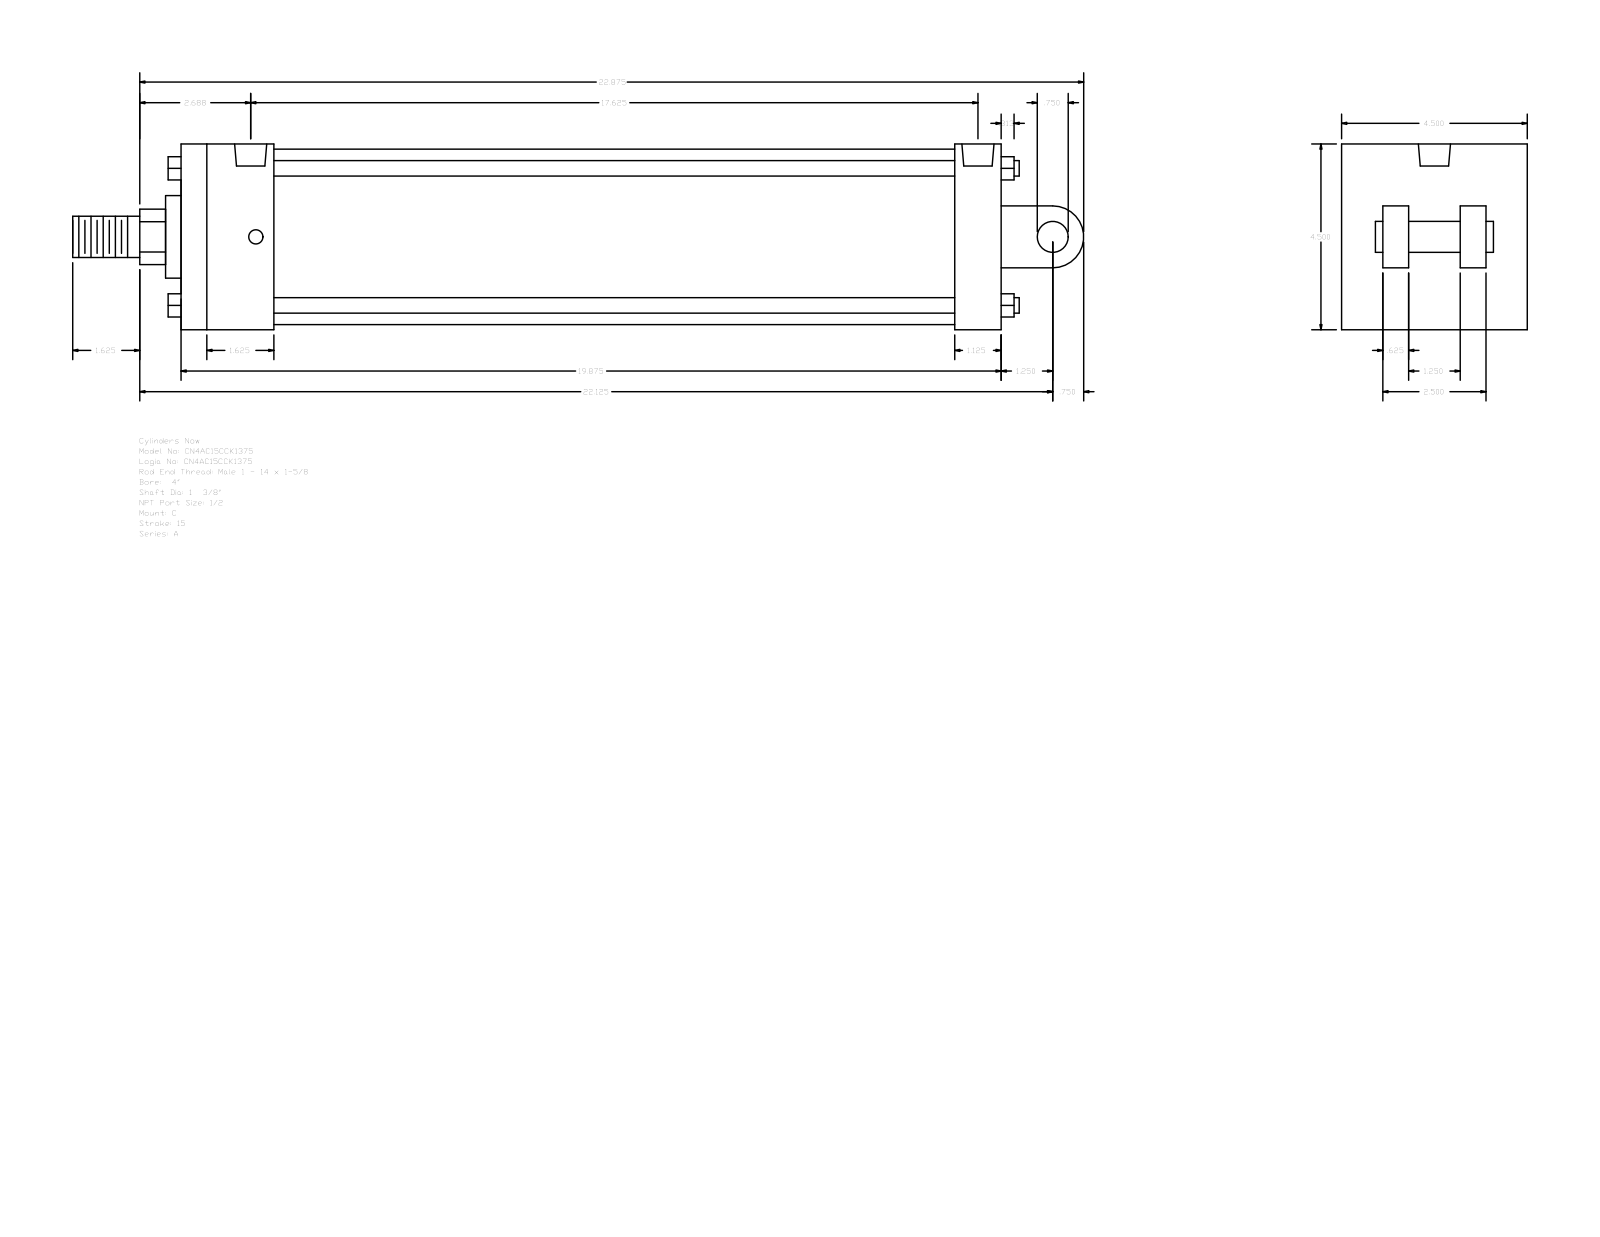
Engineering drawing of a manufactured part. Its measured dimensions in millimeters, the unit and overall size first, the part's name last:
Units: millimetres
Overall size (bounding box): 622.3 × 114.3 × 114.3
Round holes (diameter × count): ⌀8.73 ×4, ⌀19.77 ×2
Round bosses / shafts (diameter × count): ⌀9.53 ×4, ⌀107.95 ×1, ⌀50.8 ×1, ⌀34.92 ×1, ⌀25.4 ×1, ⌀19.05 ×1
Partial cylindrical surfaces — rounded edges, fillets, slot ends (radius × count): R17.06 ×1, R19.05 ×1
Main face-to-face distances: 114.3, 504.83, 57.15, 28.58, 73.03, 476.25, 419.1, 447.68, 41.27, 25.4
Hole centre spacings: 3.18, 441.32, 444.5, 447.68
Bodies: 0 solids, 135 faces (102 planar, 33 cylindrical, 0 other)
Part name (STEP PRODUCT): A_C__0400_1.375
STEP written by: GSSL Pune (CONFIG_CONTROL_DESIGN)
